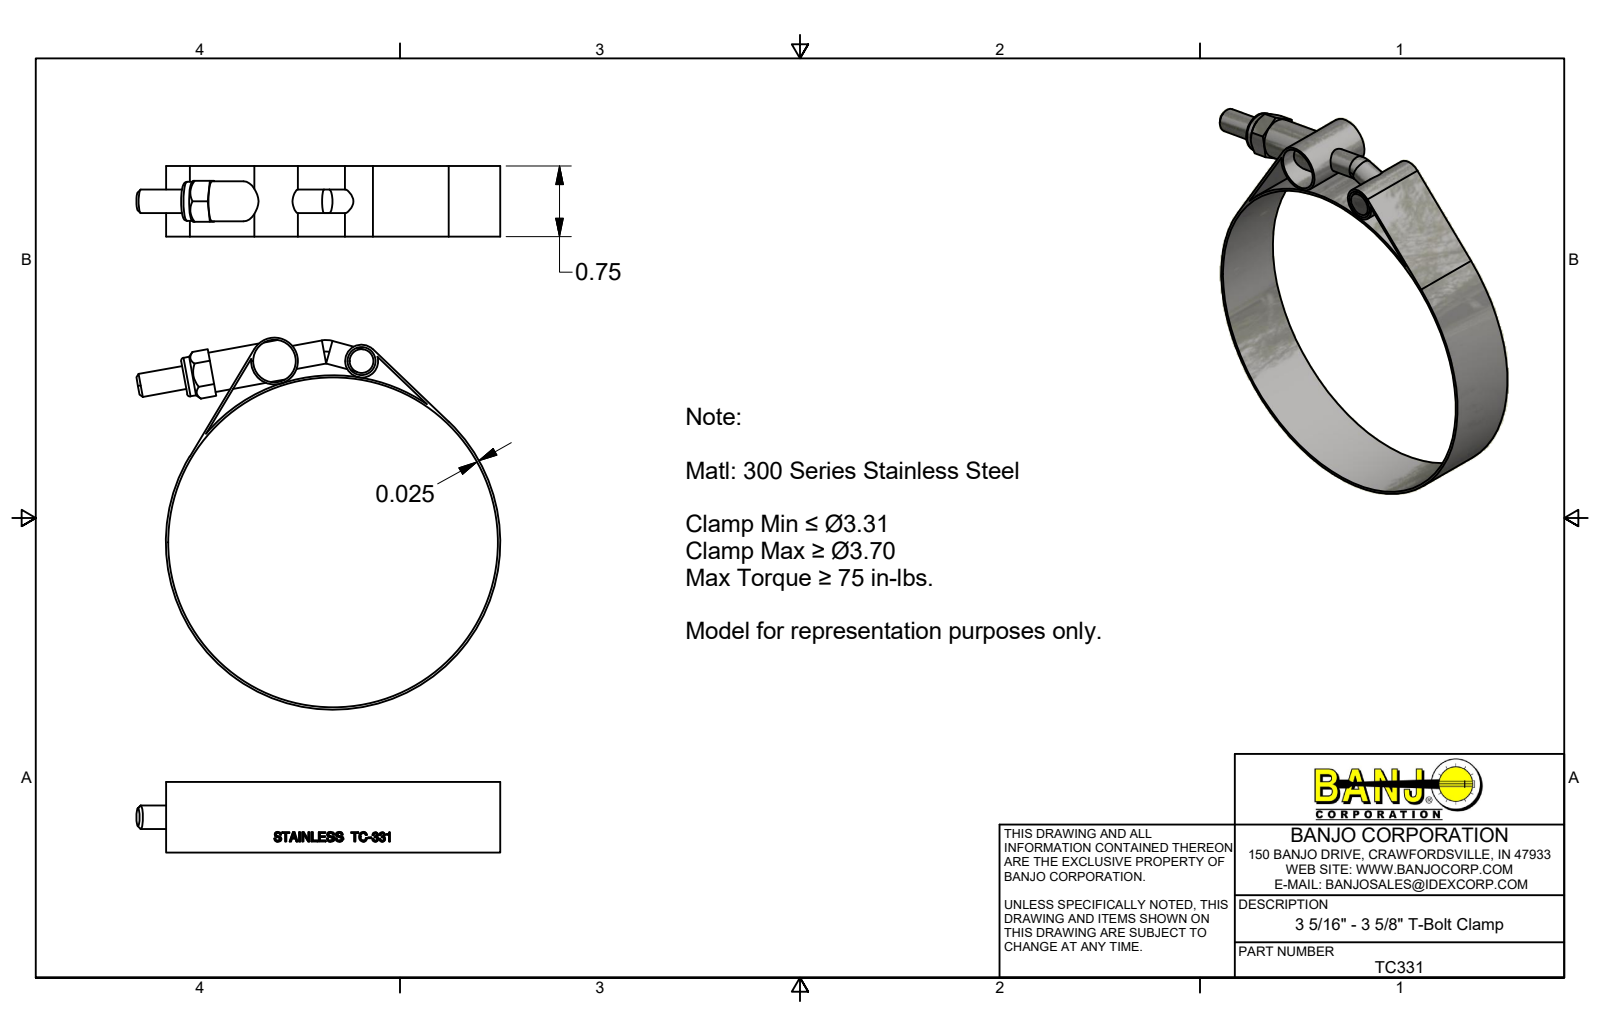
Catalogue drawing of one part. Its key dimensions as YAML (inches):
part_name: "TC331"
step_written_by: "Autodesk Inventor 2018 (AUTOMOTIVE_DESIGN)"
units: inches
bodies: {solids: 1, faces: 233, planar: 96, cylindrical: 32, other: 105}
overall_size: [3.952, 3.866, 0.75]
volume: 0.54
surface_area: 26.29
round_holes:
  - {diameter: 0.3, count: 1}
  - {diameter: 0.45, count: 1}
  - {diameter: 3.5, count: 1}
round_bosses_or_shafts:
  - {diameter: 3.55, count: 1}
  - {diameter: 0.5, count: 1}
  - {diameter: 0.425, count: 1}
  - {diameter: 0.415, count: 1}
  - {diameter: 0.35, count: 1}
  - {diameter: 0.25, count: 1}
partial_cylinders:
  - {radius: 1.77, count: 1}
face_to_face_distances: [0.025, 0.024, 0.75, 0.157, 0.592, 0.435, 0.435, 0.5, 0.8, 0.3]
hole_center_spacings: [0.925, 1.95, 2.025]
